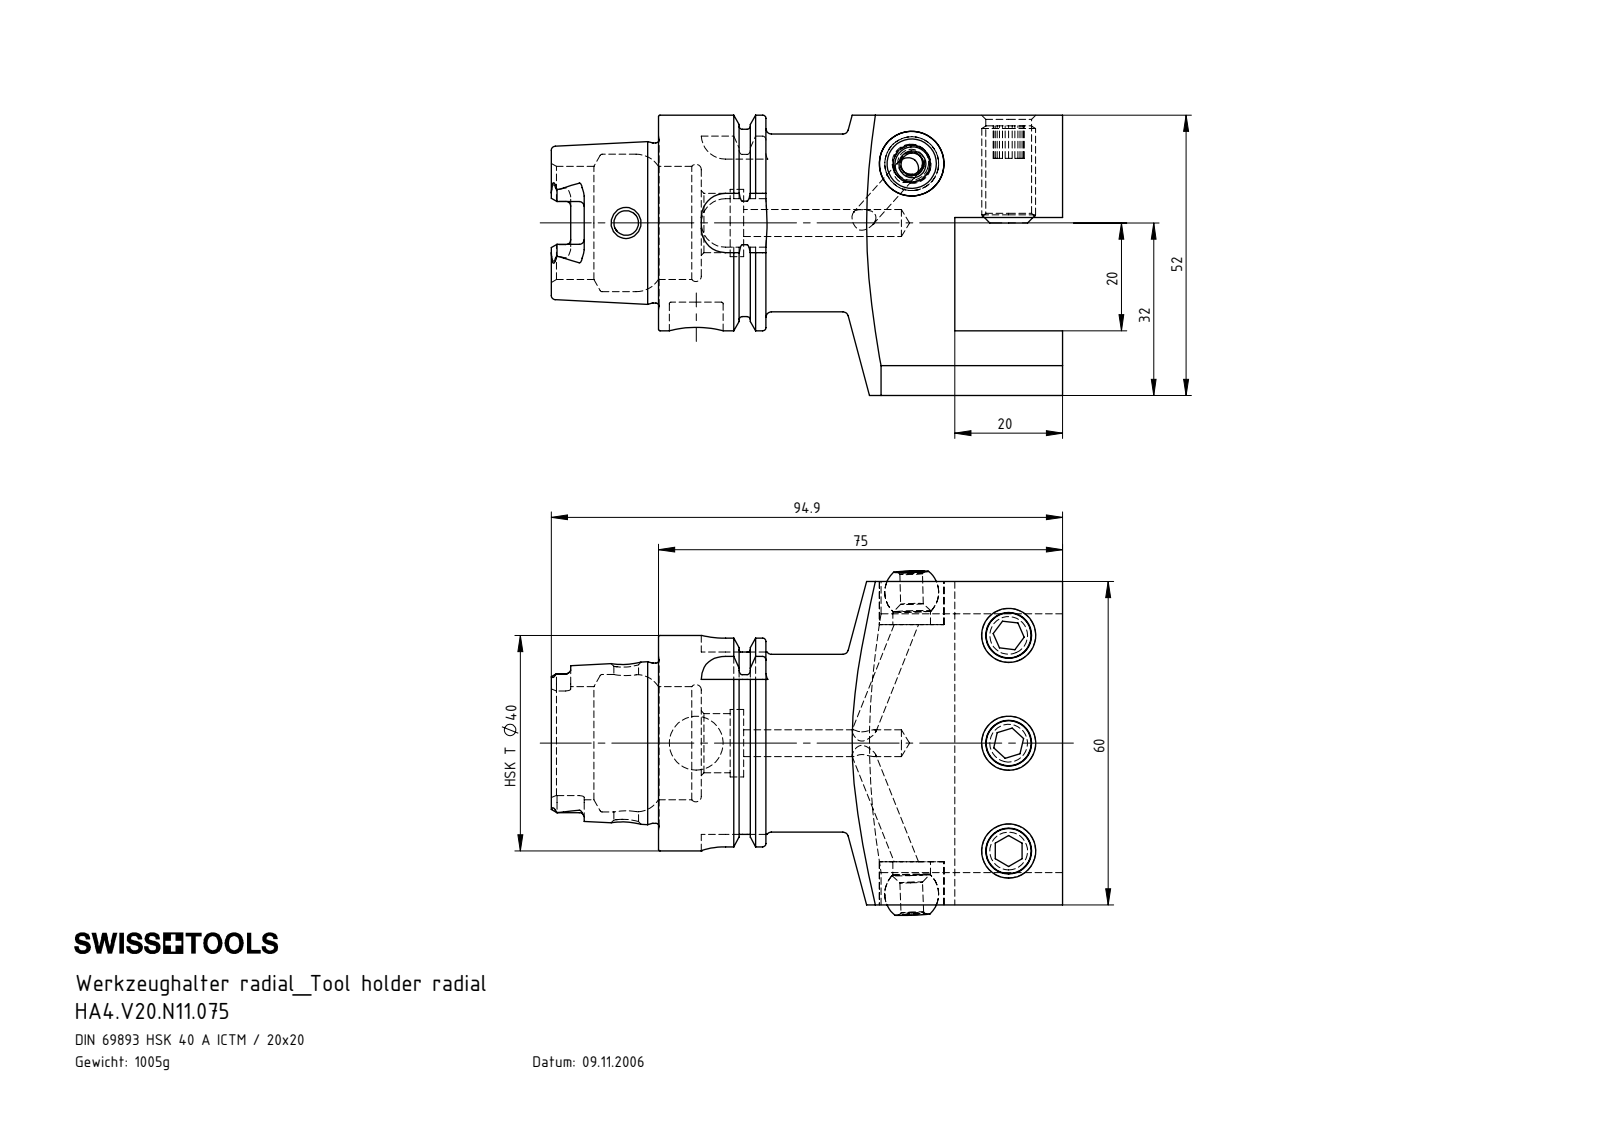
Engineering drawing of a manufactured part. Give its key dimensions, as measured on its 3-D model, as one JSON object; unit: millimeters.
{"part_name": "KU1-U12.001.010; ISO 4026 - M10 x 18; HA4-V20.N11.075_A_Fertigbearbeitung; HA4.V20.N11.075 (+2 more)", "step_written_by": "SolidWorks 2017 (AUTOMOTIVE_DESIGN)", "units": "millimeters", "bodies": {"solids": 8, "faces": 280, "planar": 89, "cylindrical": 80, "other": 111}, "overall_size": [94.9, 63.6, 52], "volume_mm3": 128597, "surface_area_mm2": 32115, "round_holes": [[4.2, 3], [8.5, 3], [4.6, 1], [5, 1], [7, 1], [10, 1], [11, 1], [12, 1], [12.5, 1], [21, 1], [25.5, 1]], "round_bosses_or_shafts": [[10, 3], [40, 1], [34.75, 1], [33, 1], [29.71, 1]], "partial_cylinders_radius": [[0.9, 6], [1.88, 4], [4.5, 4], [40, 1]], "face_to_face_distances": [52, 20, 12, 40, 60, 33, 21, 19, 8, 55], "hole_center_spacings": [20, 61.35, 40, 54.13, 58]}
